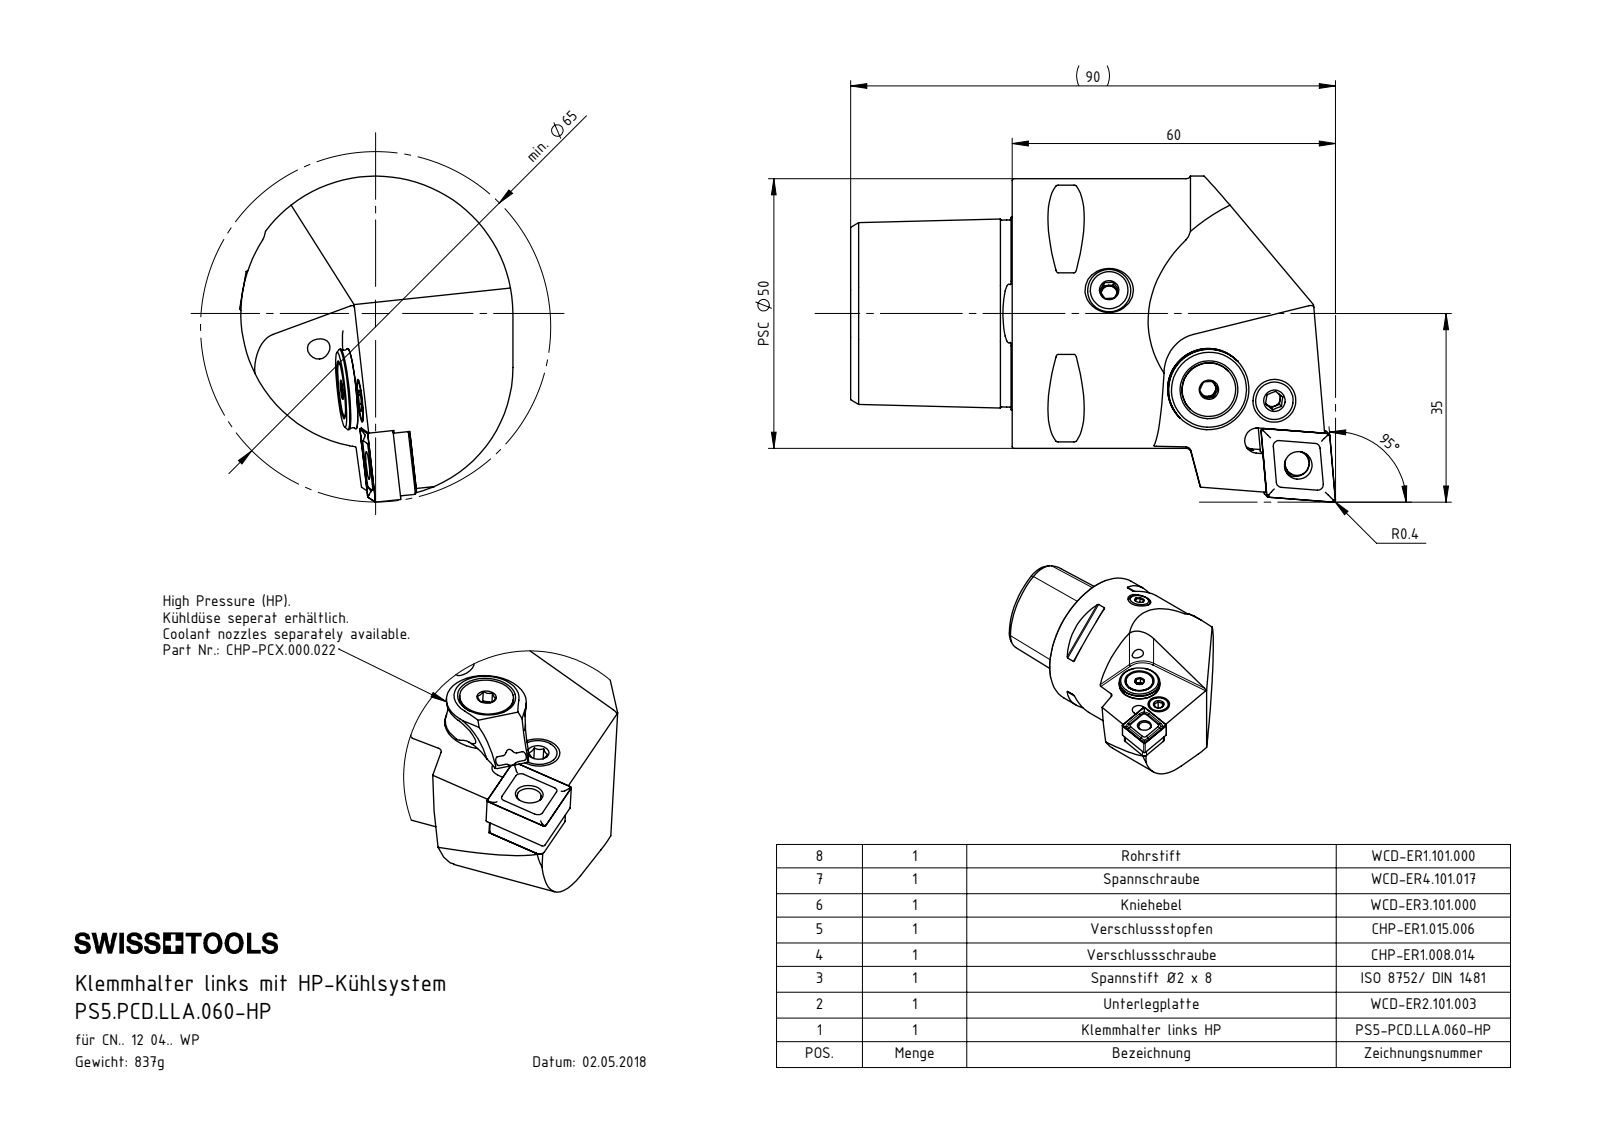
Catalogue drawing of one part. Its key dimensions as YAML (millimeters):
part_name: "CHP-ER1.015.006; DIN 3771 - 13x1; CHP-ER1.008.014_A; CHP-ER1.015.006_A (+8 more)"
step_written_by: "SolidWorks 2017 (AUTOMOTIVE_DESIGN)"
units: millimeters
bodies: {solids: 10, faces: 322, planar: 130, cylindrical: 71, other: 121}
overall_size: [90, 60.03, 50.5]
volume: 106237
surface_area: 24382
round_holes:
  - {diameter: 4.2, count: 3}
  - {diameter: 5, count: 2}
  - {diameter: 7, count: 2}
  - {diameter: 1.2, count: 1}
  - {diameter: 2, count: 1}
  - {diameter: 2.5, count: 1}
  - {diameter: 3, count: 1}
  - {diameter: 4, count: 1}
  - {diameter: 5.16, count: 1}
  - {diameter: 5.2, count: 1}
  - {diameter: 6.1, count: 1}
  - {diameter: 6.4, count: 1}
round_bosses_or_shafts:
  - {diameter: 8, count: 2}
  - {diameter: 50, count: 1}
  - {diameter: 15, count: 1}
  - {diameter: 13.4, count: 1}
  - {diameter: 10, count: 1}
  - {diameter: 7.9, count: 1}
  - {diameter: 6.4, count: 1}
  - {diameter: 5.5, count: 1}
partial_cylinders:
  - {radius: 0.5, count: 10}
  - {radius: 0.4, count: 4}
  - {radius: 1, count: 4}
  - {radius: 2.5, count: 2}
  - {radius: 2.1, count: 1}
  - {radius: 2.2, count: 1}
  - {radius: 2.35, count: 1}
  - {radius: 2.9, count: 1}
face_to_face_distances: [30, 4.5, 4.46, 19.18, 3.14, 3.18, 7.64, 44.4, 12.71, 11.69]
hole_center_spacings: [4.5, 10.43, 12.22, 20.03, 20.09, 23.56, 12.81, 12.86]
